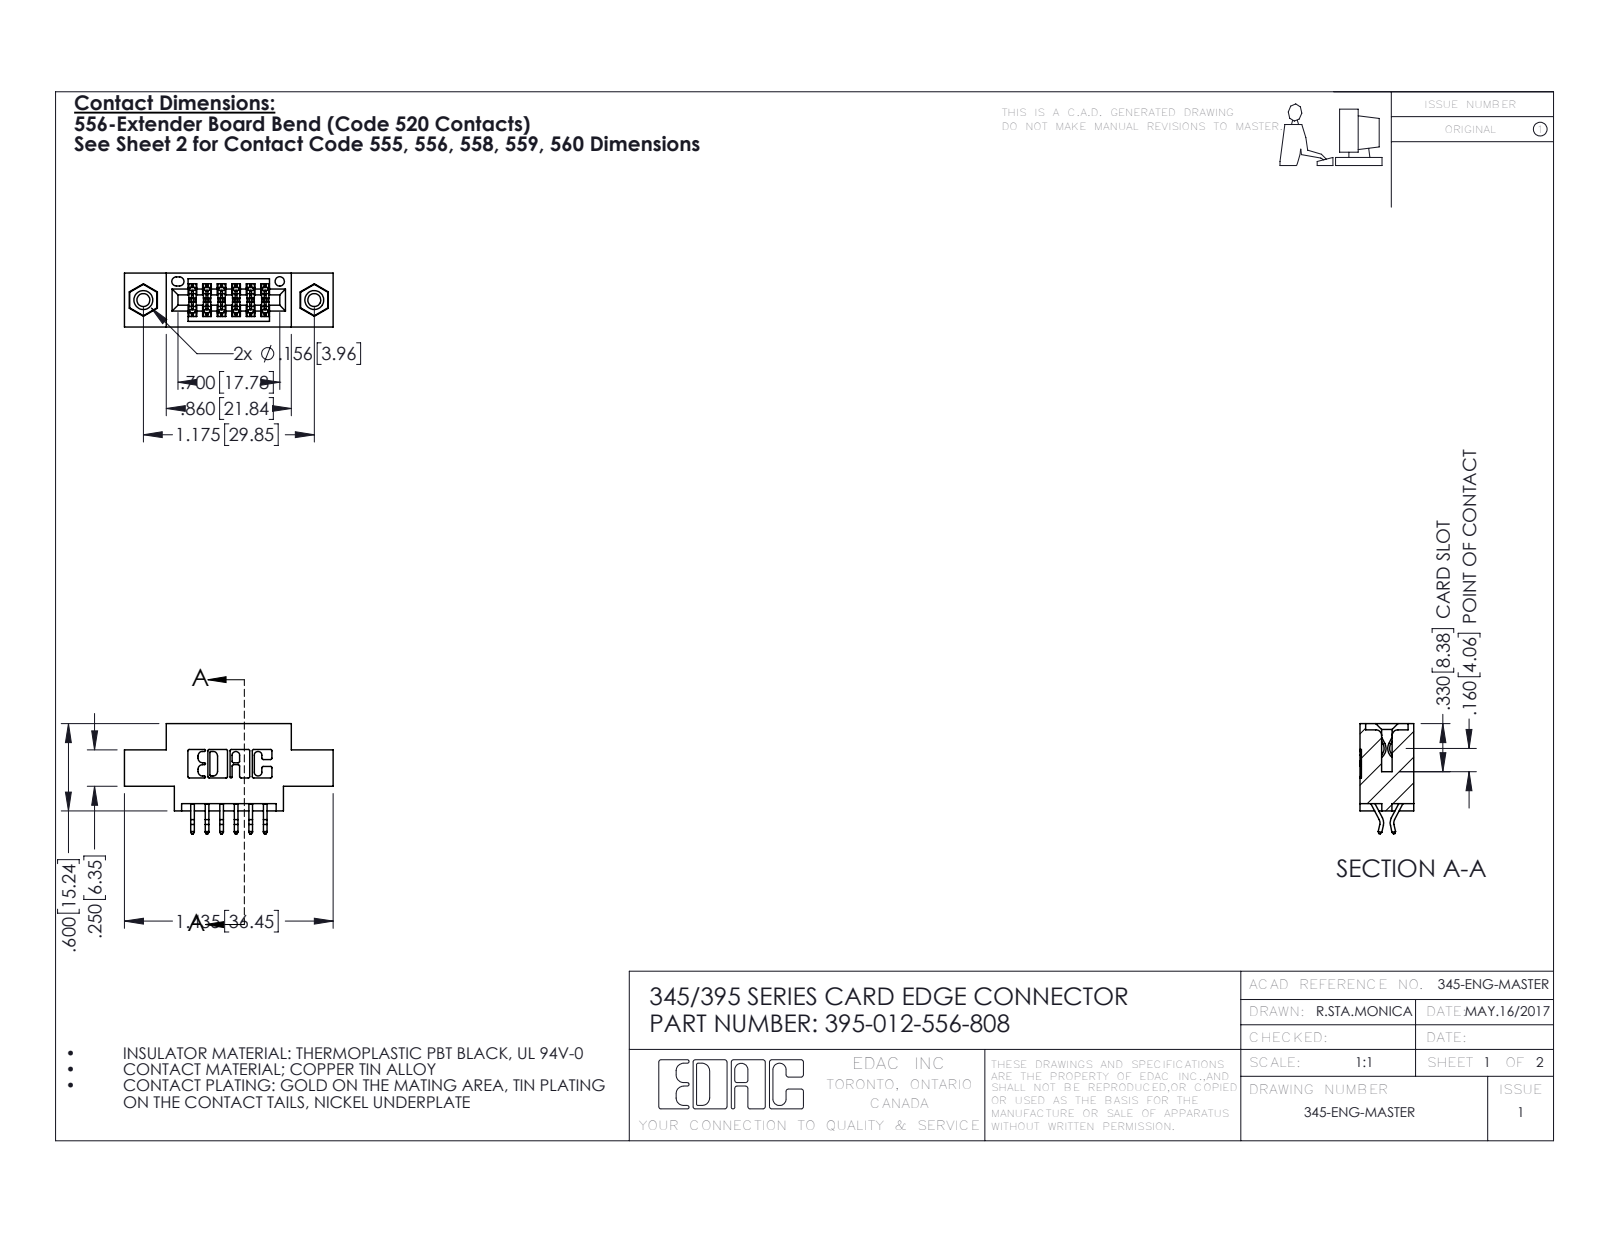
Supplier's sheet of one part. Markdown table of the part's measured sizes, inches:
| quantity | value |
| --- | --- |
| part name | 345 Part_0.170 Offset - 0.156 Dia-TI; 395-012-556-808; 345-250-001_345-250-003-102; 345-292-001_556 Tail |
| STEP written by | SolidWorks 2016 (CONFIG_CONTROL_DESIGN) |
| units | inches |
| bodies | 15 solids, 862 faces (560 planar, 286 cylindrical, 16 other) |
| overall size | 1.435 × 0.757 × 0.37 |
| volume | 0.188 in³ |
| surface area | 6.217 in² |
| round holes (diameter × count) | 0.089 × 2, 0.125 × 2, 0.156 × 2, 0.064 × 1 |
| round bosses / shafts (diameter × count) | 0.155 × 2 |
| partial cylindrical surfaces (radius × count) | 0.01 × 22, 0.006 × 18, 0.007 × 6, 0.031 × 6, 0.026 × 3, 0.01 × 2, 0.014 × 2, 0.019 × 2 |
| main face-to-face distances | 0.37, 0.2, 0.072, 0.298, 0.1, 0.025, 0.098, 0.272, 0.06, 0.3 |
| hole center spacings | 0.27, 0.946, 1.175 |
